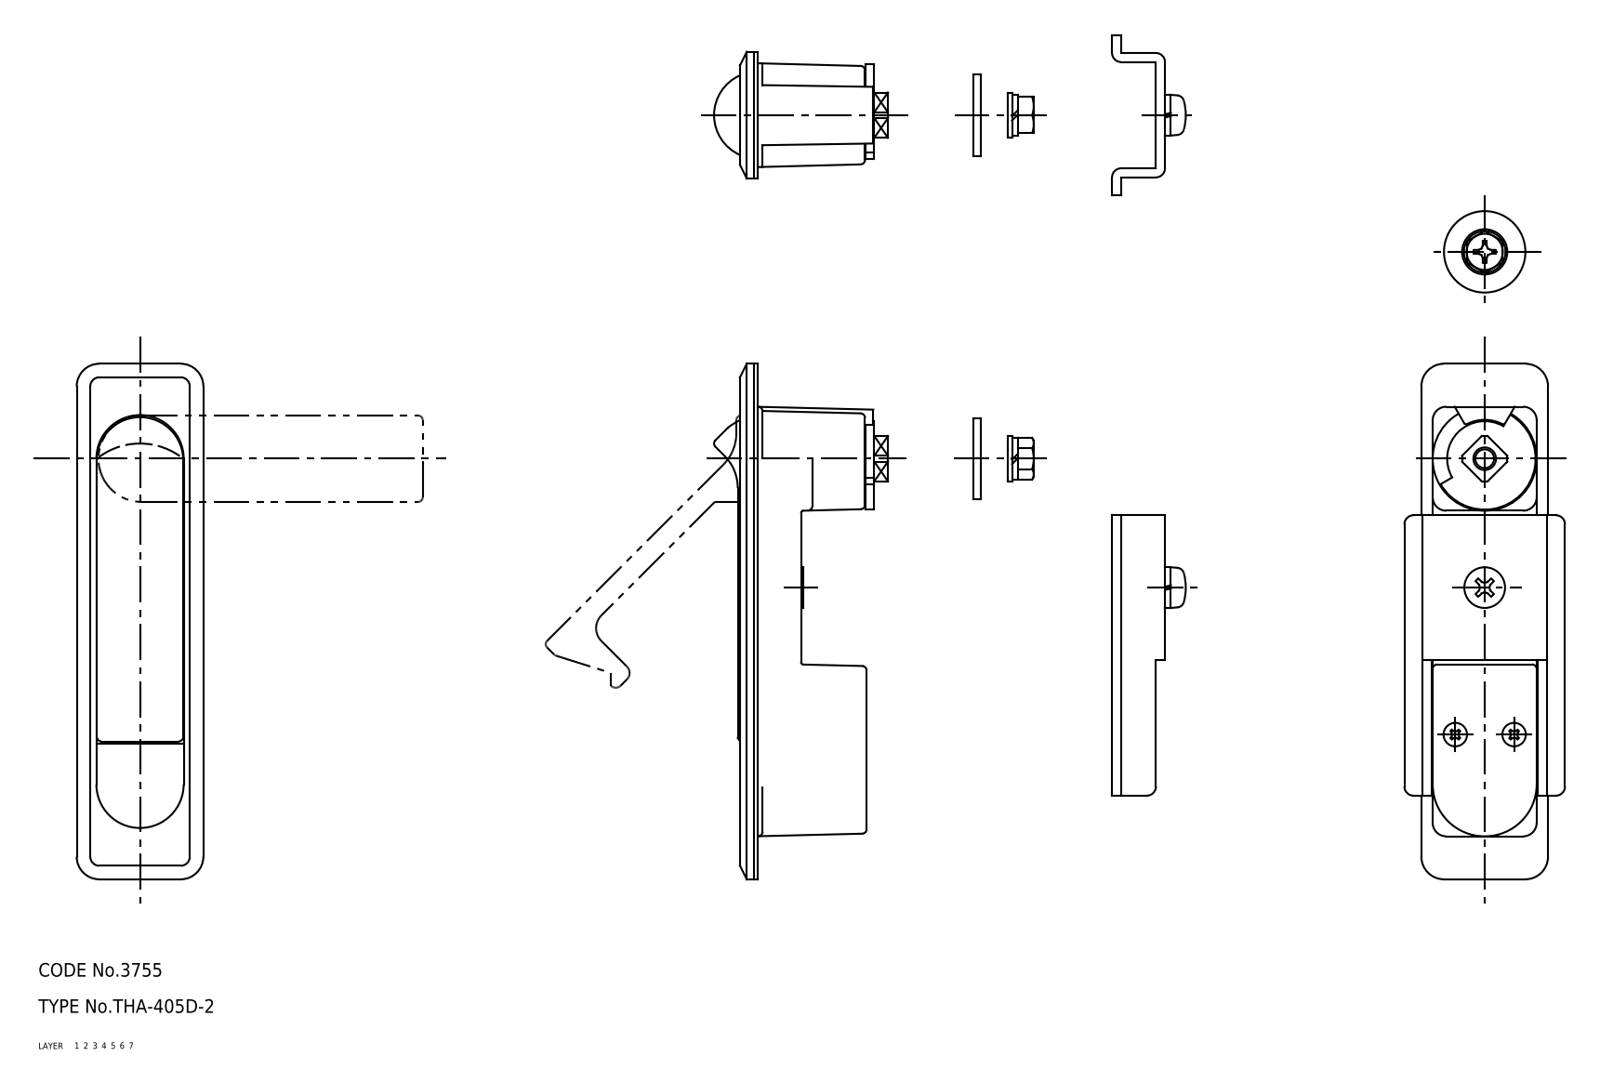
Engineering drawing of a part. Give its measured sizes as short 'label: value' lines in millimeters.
name: 67129352; 67129365; 67129378; 67129391 (+6 more)
written by: CADfix (AUTOMOTIVE_DESIGN)
unit: mm
bodies: 10 solids, 429 faces (0 planar, 0 cylindrical, 429 other)
size: 114 × 43.5 × 35.5
volume: 44 533 mm³; area: 35 985 mm²
